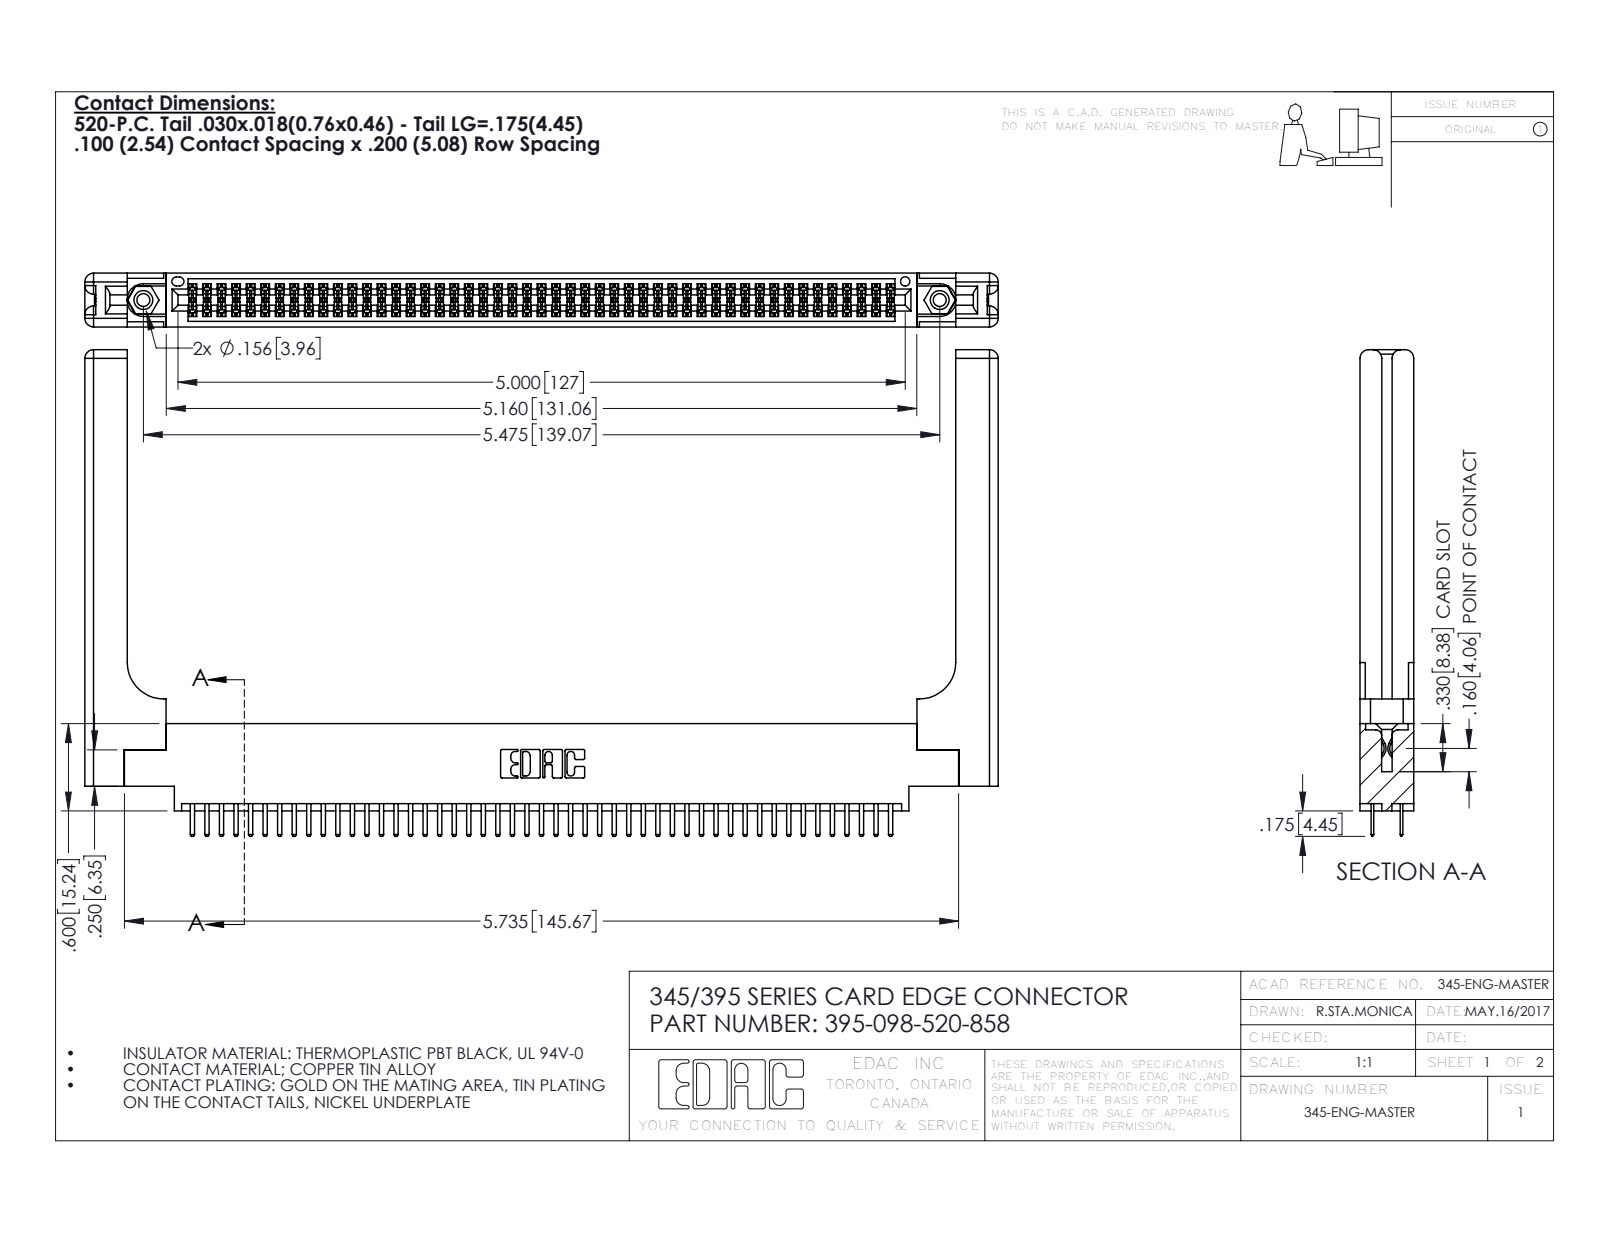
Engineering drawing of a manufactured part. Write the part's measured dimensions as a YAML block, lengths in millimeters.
part_name: "345-292-001_345-293-120; 395-098-520-858; 345-220-058_345-220-058; 345 Part_0.170 Offset - 0.156 Dia-TH (+1 more)"
step_written_by: "SolidWorks 2016 (CONFIG_CONTROL_DESIGN)"
units: millimeters
bodies: {solids: 103, faces: 5678, planar: 3662, cylindrical: 1956, other: 60}
overall_size: [159.5, 85, 9.4]
volume: 23880
surface_area: 28010
round_holes:
  - {diameter: 2.3, count: 2}
  - {diameter: 3.2, count: 2}
  - {diameter: 4, count: 2}
  - {diameter: 1.6, count: 1}
round_bosses_or_shafts:
  - {diameter: 3.9, count: 2}
partial_cylinders:
  - {radius: 0.2, count: 147}
  - {radius: 0.3, count: 102}
  - {radius: 0.3, count: 22}
  - {radius: 1.5, count: 16}
  - {radius: 0.2, count: 6}
  - {radius: 0.8, count: 6}
  - {radius: 0.7, count: 3}
  - {radius: 0.4, count: 2}
face_to_face_distances: [9.4, 1.8, 7.6, 5.1, 2.5, 6.9, 0.6, 5.7, 3.8, 3.8]
hole_center_spacings: [6.9, 133.1, 139.1]
